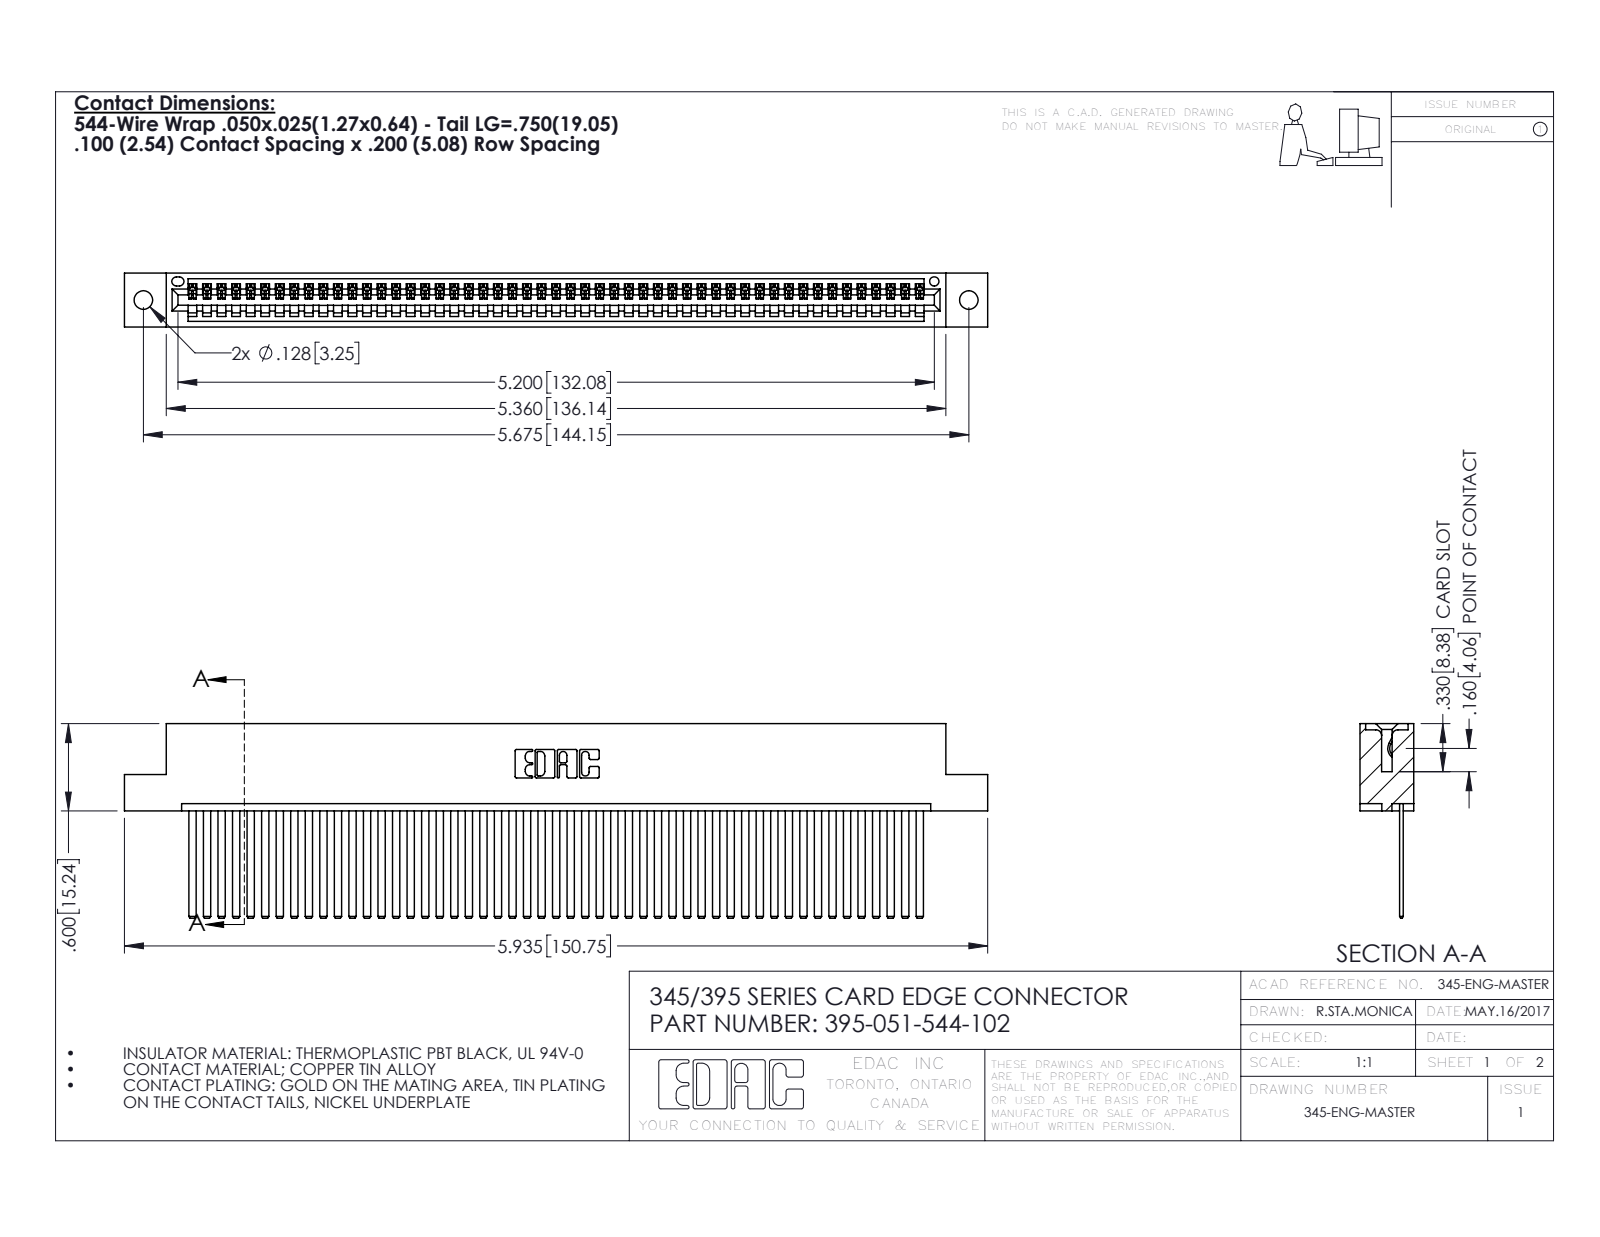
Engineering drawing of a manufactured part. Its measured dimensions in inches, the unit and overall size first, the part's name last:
Units: inches
Overall size (bounding box): 5.935 × 1.337 × 0.37
Round holes (diameter × count): ⌀0.128 ×2, ⌀0.064 ×1
Partial cylindrical surfaces — rounded edges, fillets, slot ends (radius × count): R0.006 ×102, R0.01 ×22, R0.007 ×6, R0.031 ×6, R0.026 ×3, R0.031 ×2, R0.04 ×2, R0.014 ×1
Main face-to-face distances: 0.072, 0.298, 0.025, 0.098, 0.272, 0.37, 0.2, 0.225, 0.149, 0.072
Hole centre spacings: 0.27, 5.439, 5.675
Volume: 0.912 in³ · Surface area: 33.3 in²
Bodies: 52 solids, 2778 faces (1916 planar, 862 cylindrical, 0 other)
Part name (STEP PRODUCT): 345-292-001_345-293-144; 345 Part_Flush Mounting Lugs - 0.128 Dia; 395-051-544-102
STEP written by: SolidWorks 2016 (CONFIG_CONTROL_DESIGN)
